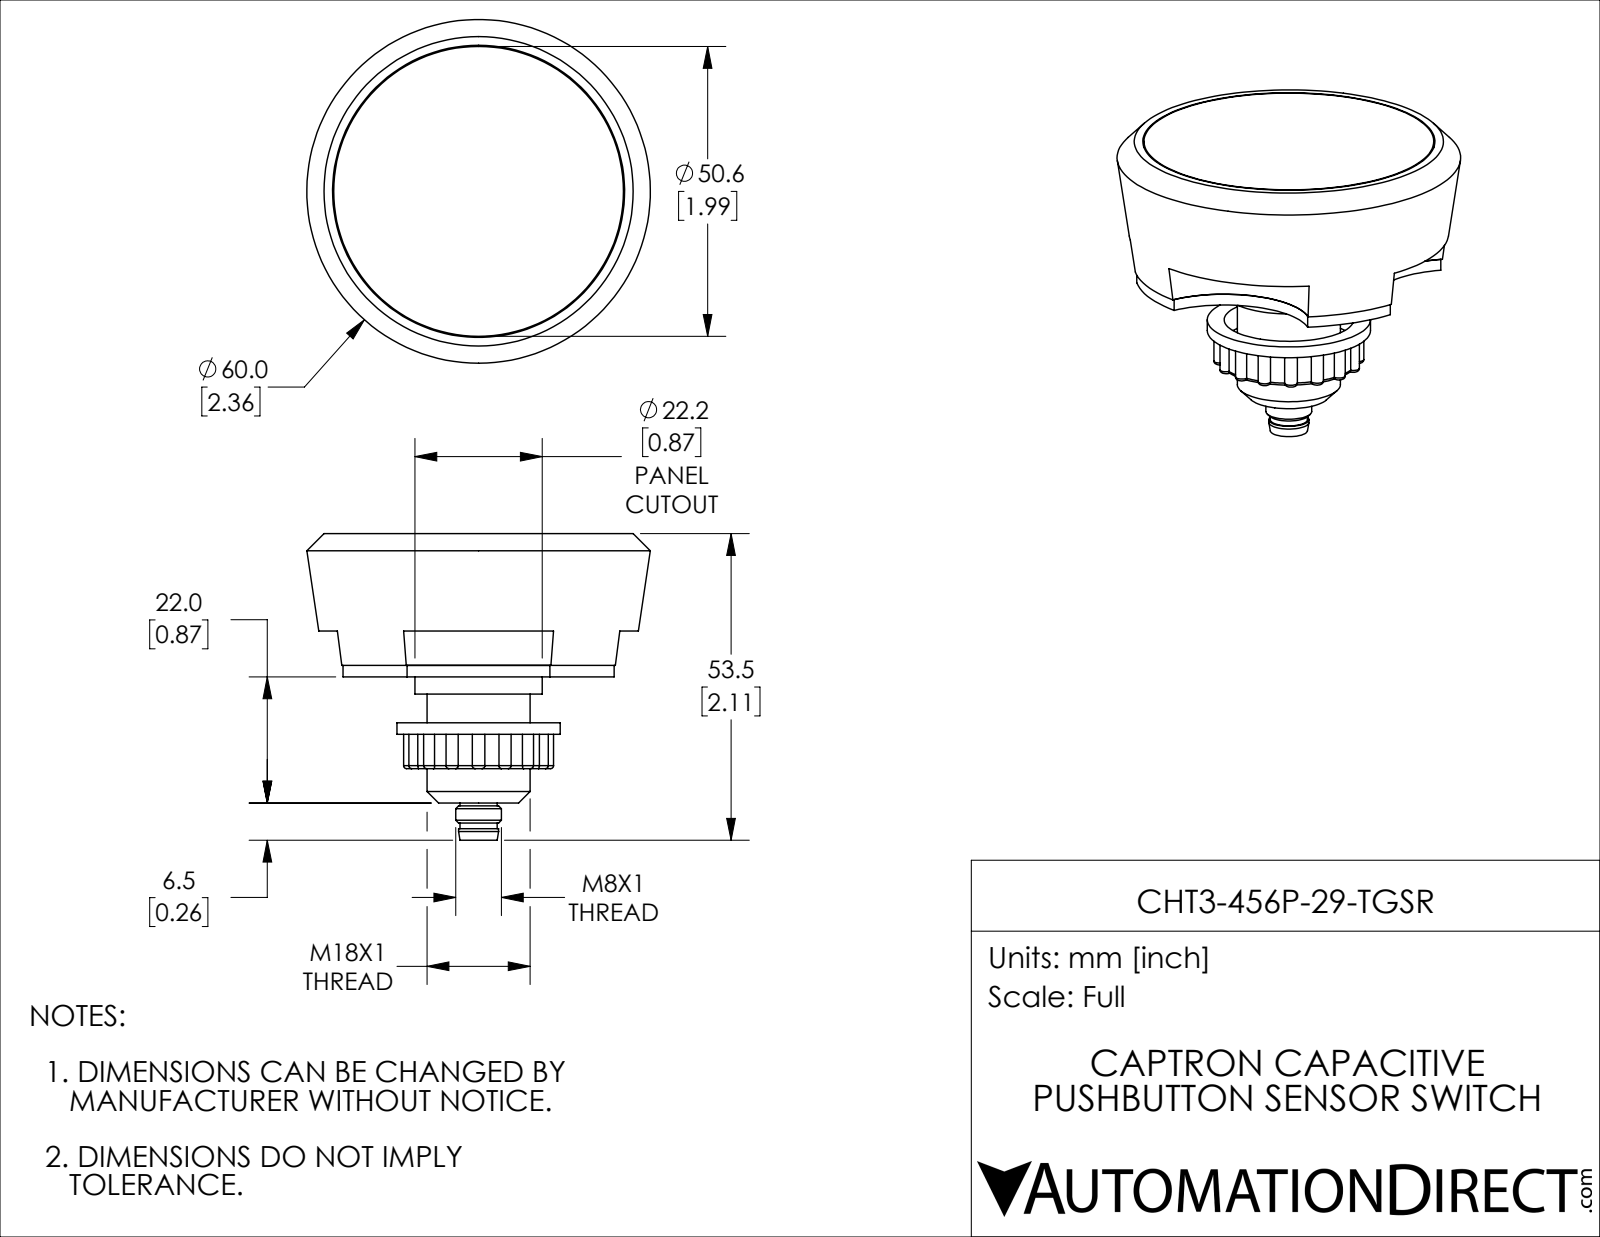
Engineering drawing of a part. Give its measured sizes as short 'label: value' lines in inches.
name: CHT3-456P-29-TGSR
written by: SolidWorks 2019 (CONFIG_CONTROL_DESIGN)
unit: in
bodies: 9 solids, 197 faces (27 planar, 95 cylindrical, 75 other)
size: 2.362 × 2.362 × 2.106
volume: 3.903 in³; area: 31.91 in²
holes: 1× ⌀0.236, 1× ⌀0.669, 1× ⌀0.89, 1× ⌀2.008
bosses: 4× ⌀0.039, 1× ⌀1.992, 1× ⌀1.122, 1× ⌀0.874, 1× ⌀0.709, 1× ⌀0.315, 1× ⌀0.276, 1× ⌀0.256
rounds: 16× R0.043, 4× R0.591, 1× R0.472, 1× R1.053
face distances: 0.906, 0.795, 0.11, 0.02, 0.815, 0.091, 0.079, 0.315, 0.874, 0.894
